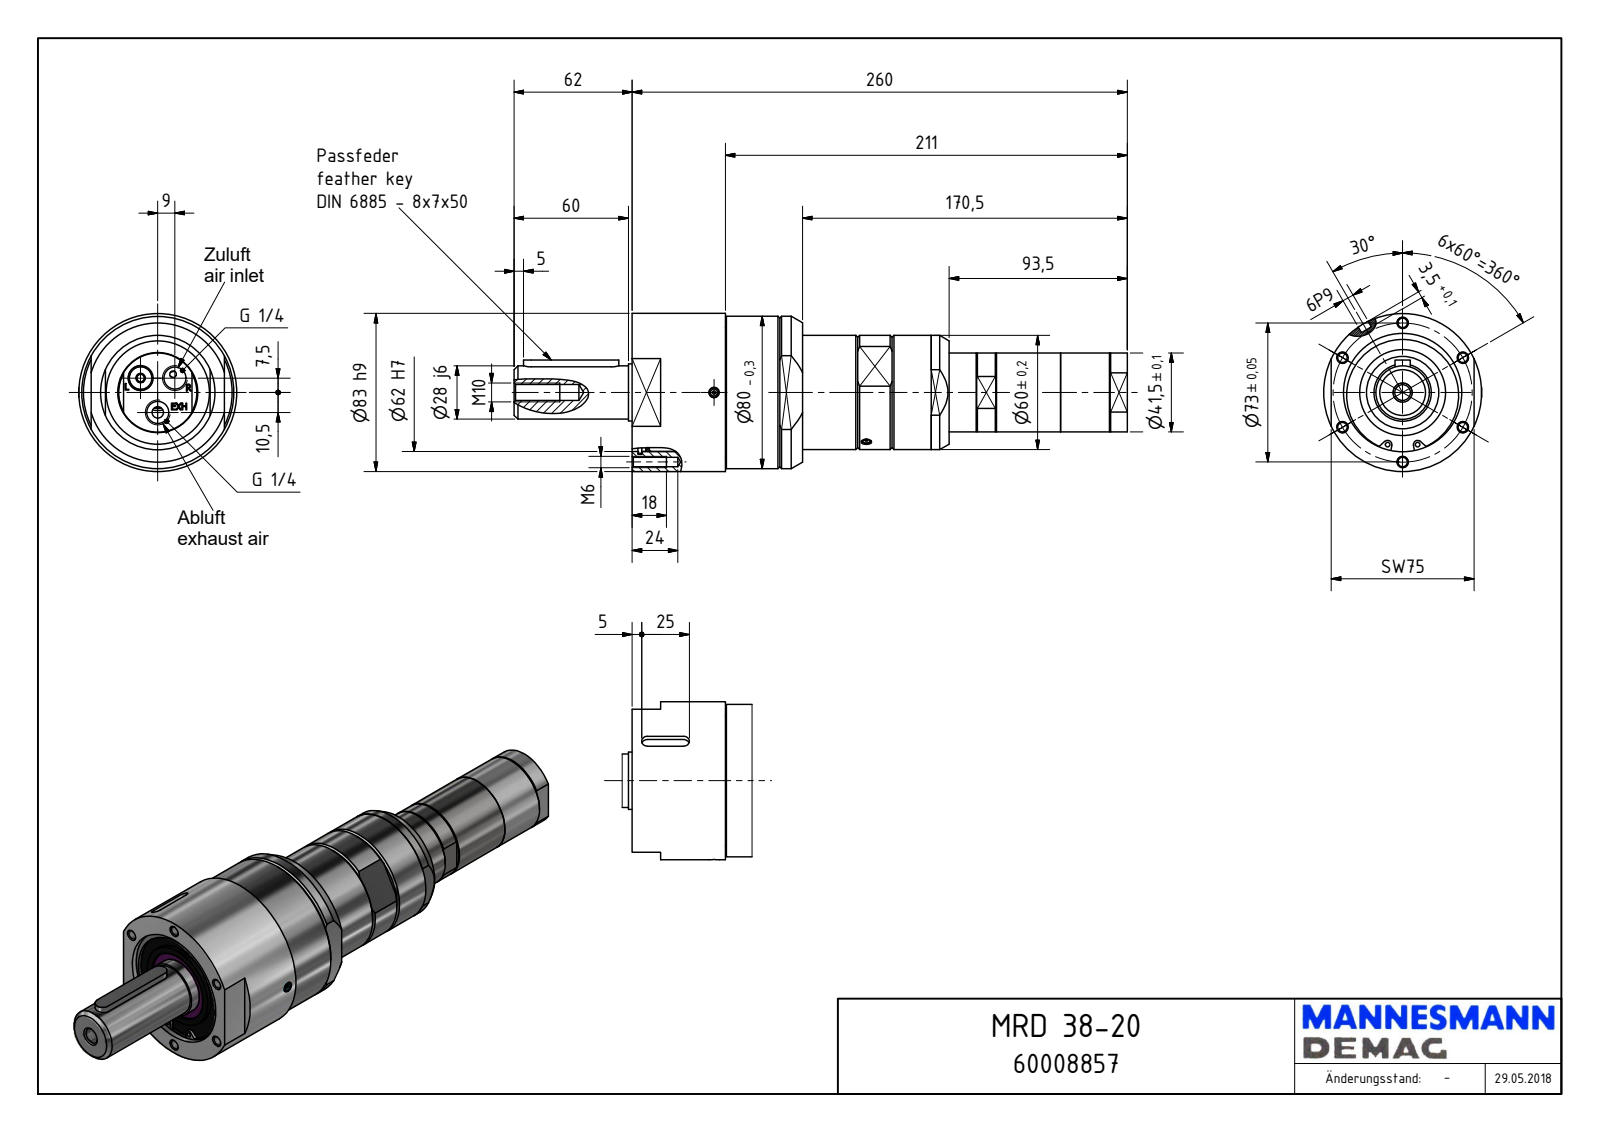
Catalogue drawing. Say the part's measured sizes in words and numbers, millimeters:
The part is named "MRD 38-20_60008855". Its 3-D file was written by "Autodesk Inventor 2018 (AUTOMOTIVE_DESIGN)". It is 1 solid with 565 faces: 239 planar, 259 cylindrical and 67 other. Overall it measures 322 by 83 by 83 millimeters. Its volume is 820 220 cubic millimeters and its surface area 80 619 square millimeters. Round holes: 6 of diameter 4.92, 3 of diameter 4, 3 of diameter 11.45, 2 of diameter 1.55, 2 of diameter 5.5, 1 of diameter 8.38, 1 of diameter 38, 1 of diameter 40, 1 of diameter 42, 1 of diameter 61.16, 1 of diameter 62, 1 of diameter 65. Round bosses or shafts: 2 of diameter 5, 2 of diameter 3.6, 1 of diameter 83, 1 of diameter 80, 1 of diameter 68.18, 1 of diameter 67, 1 of diameter 60, 1 of diameter 45. Partial cylindrical surfaces (rounded edges, fillets, slot ends): 94 of radius 3.5, 2 of radius 3, 2 of radius 4, 1 of radius 24.73, 1 of radius 24.96, 1 of radius 33.32. The main face-to-face distances are 49, 2.5, 0.5, 5, 44, 89.5, 84.5, 40.5, 49.5, 44.5. The hole center spacings are 36.5, 63.22, 73, 11.72, 20.12, 25.04, 30.36, 32.55.
